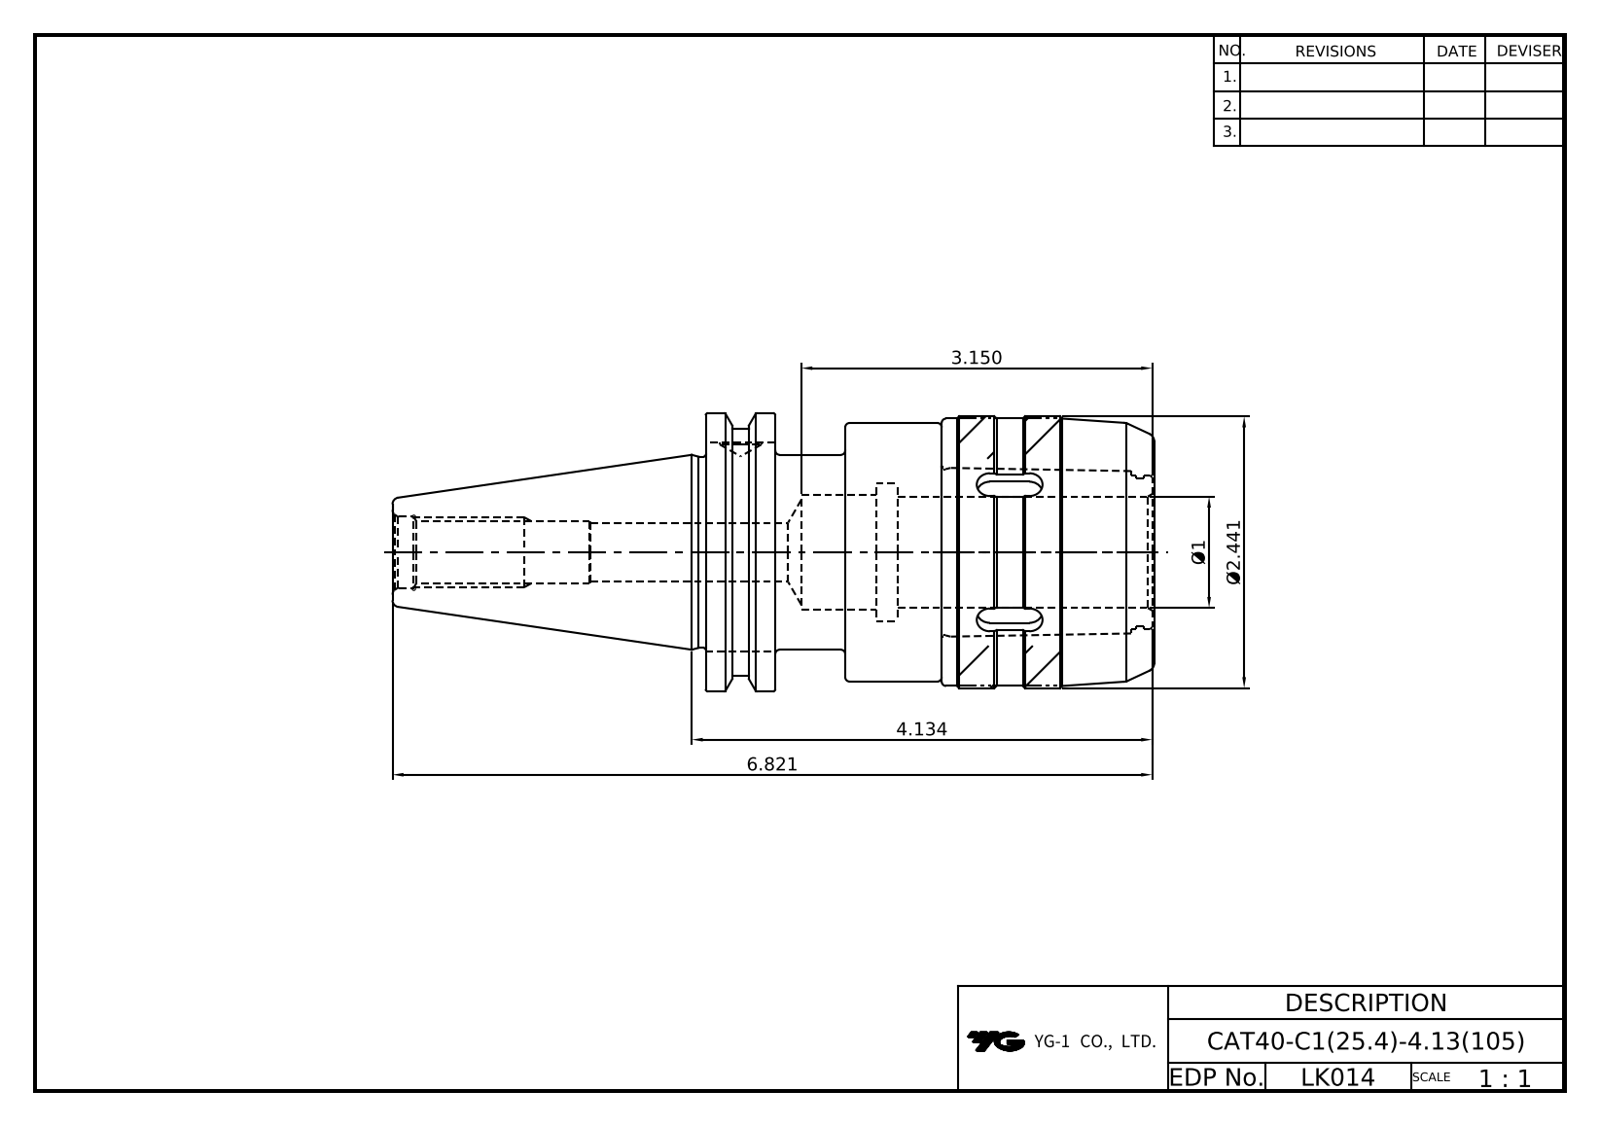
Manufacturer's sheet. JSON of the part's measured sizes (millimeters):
{"part_name": "LO_CAT40-C1-4_13-LK014; C25-CAP-LAYOUT; LO_CAT40-C1-4_13-LK014_ASM", "step_written_by": "CREO PARAMETRIC BY PTC INC, 2018100 (CONFIG_CONTROL_DESIGN)", "units": "millimeters", "bodies": {"solids": 2, "faces": 210, "planar": 62, "cylindrical": 64, "other": 84}, "overall_size": [173.75, 63.5, 62], "volume_mm3": 264539, "surface_area_mm2": 62433, "round_holes": [[9.53, 1], [13.5, 1], [14, 1], [15.88, 1], [16.3, 1], [25.4, 1], [26, 1], [31.6, 1], [44.5, 1]], "round_bosses_or_shafts": [[63.5, 1], [62, 1], [61, 1], [59, 1], [56.3, 1], [44.45, 1], [43.6, 1], [39.2, 1]], "partial_cylinders_radius": [[3, 6]], "face_to_face_distances": [37.95, 15.88, 53.83, 22, 31.83, 15.95, 102.33, 86.45, 70.5, 48.5]}
